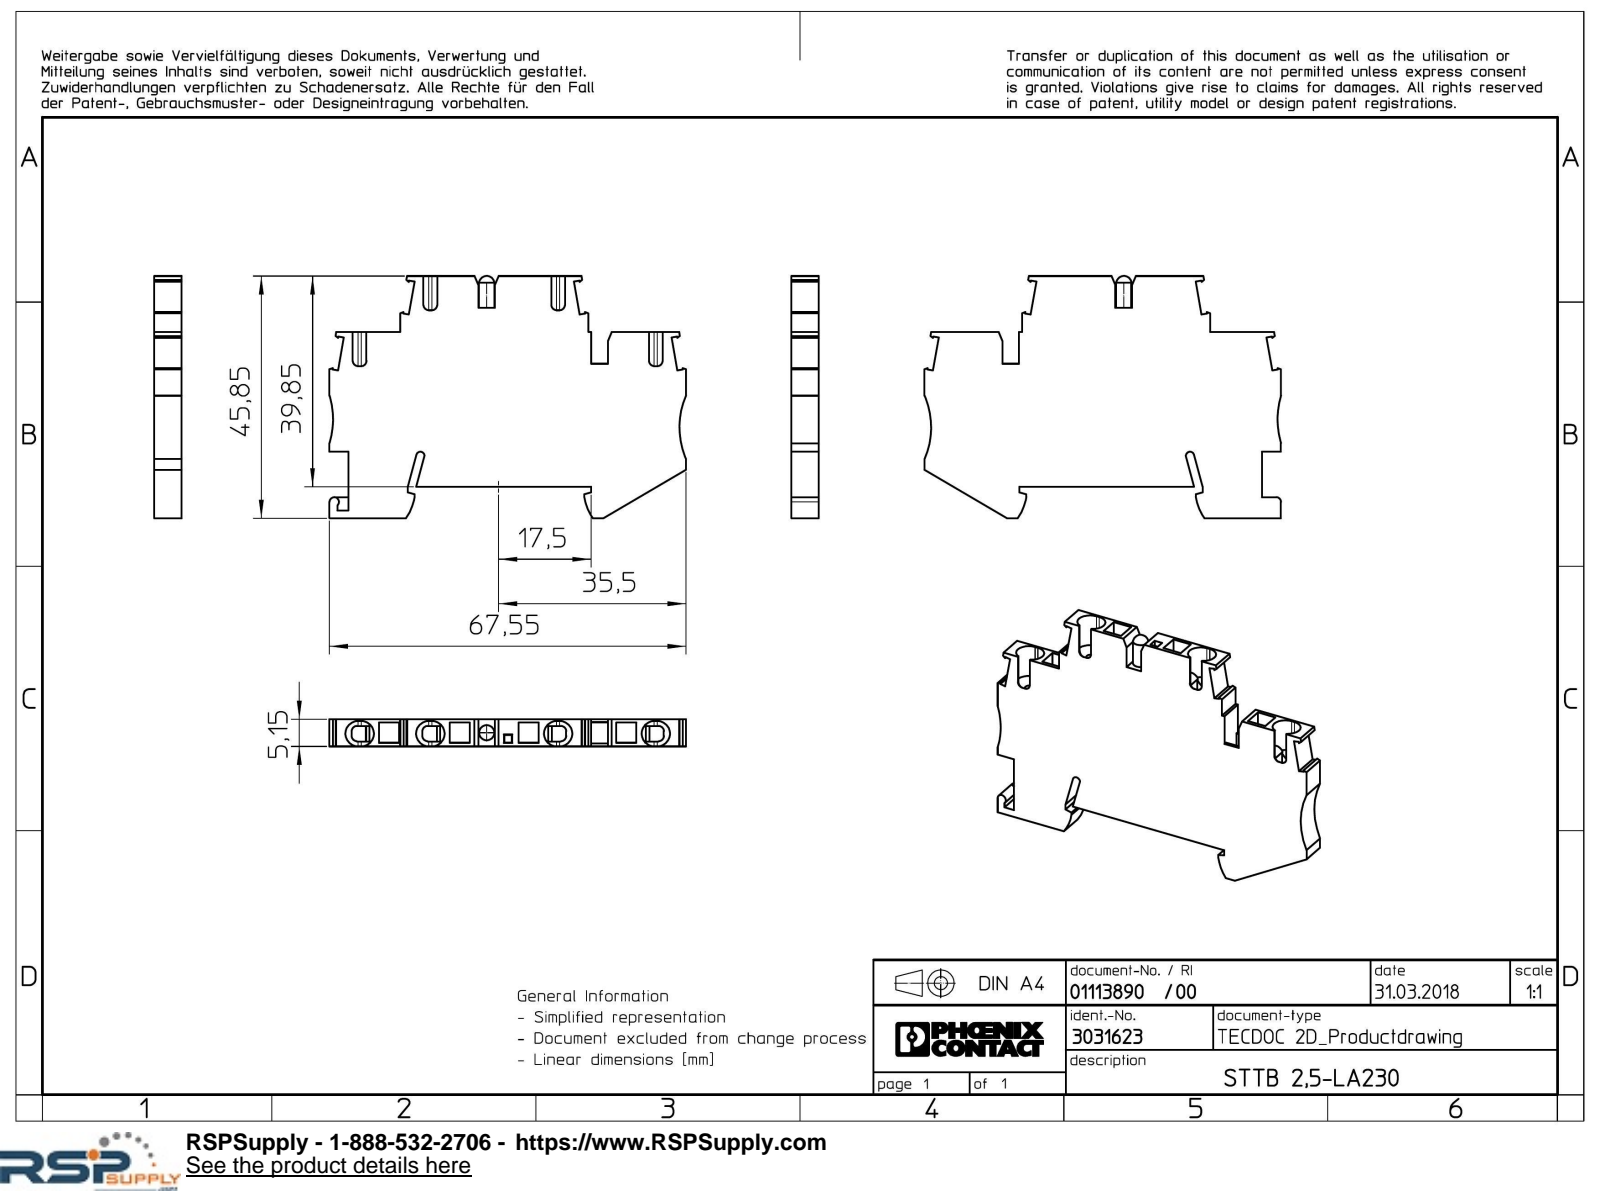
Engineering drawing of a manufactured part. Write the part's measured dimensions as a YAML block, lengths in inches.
part_name: "STTB25_LA230_select"
step_written_by: "Creo Elements/Direct Modeling 20.1A 29-Sep-2018 (C) Parametric Technology GmbH (AUTOMOTIVE_DESIGN)"
units: inches
bodies: {solids: 1, faces: 200, planar: 153, cylindrical: 33, other: 14}
overall_size: [2.659, 1.805, 0.203]
volume: 0.648
surface_area: 11.64
round_bosses_or_shafts:
  - {diameter: 0.114, count: 1}
partial_cylinders:
  - {radius: 0.039, count: 16}
  - {radius: 0.094, count: 8}
  - {radius: 0.374, count: 2}
  - {radius: 0.591, count: 2}
  - {radius: 0.031, count: 1}
  - {radius: 0.035, count: 1}
  - {radius: 0.47, count: 1}
face_to_face_distances: [0.203, 0.026, 0.124, 0.15, 0.177, 1.152, 0.175, 0.236, 0.52, 0.028]
